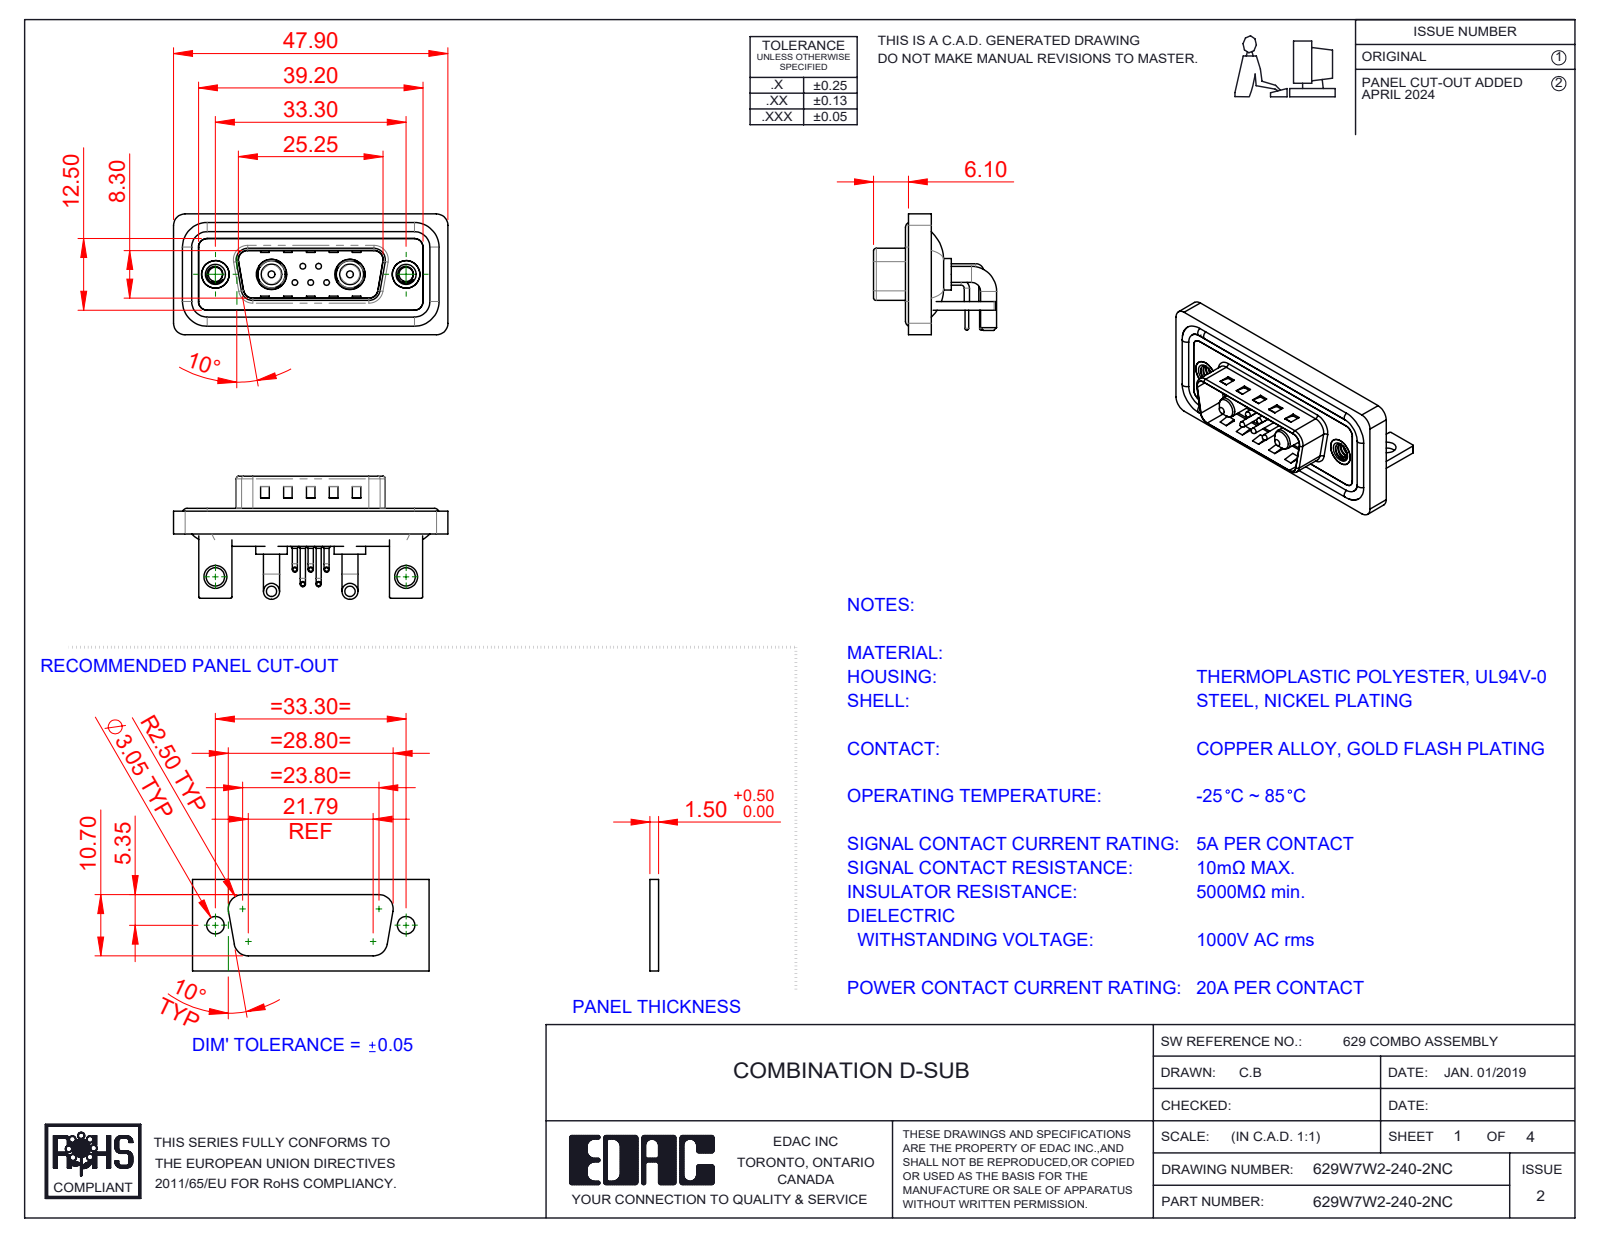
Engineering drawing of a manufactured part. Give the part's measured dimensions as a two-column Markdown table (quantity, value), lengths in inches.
| quantity | value |
| --- | --- |
| part name | 629Combo Contact Row 1; 629Combo Stabilizer Bracket; 629Combo Contact Row 2; 629Combo Waterproof Housing_15 Contacts (+6 more) |
| STEP written by | SolidWorks 2023 (CONFIG_CONTROL_DESIGN) |
| units | inches |
| bodies | 18 solids, 1121 faces (537 planar, 424 cylindrical, 160 other) |
| overall size | 1.886 × 0.846 × 0.831 |
| volume | 0.363 in³ |
| surface area | 15.08 in² |
| round holes (diameter × count) | 0.03 × 5, 0.063 × 5, 0.079 × 5, 0.098 × 2, 0.126 × 2, 0.157 × 2, 0.189 × 2, 0.191 × 2, 0.197 × 2, 0.209 × 2 |
| round bosses / shafts (diameter × count) | 0.035 × 10, 0.059 × 5, 0.039 × 5, 0.026 × 5, 0.11 × 4, 0.063 × 4, 0.217 × 2, 0.205 × 2 |
| partial cylindrical surfaces (radius × count) | 0.079 × 21, 0.059 × 18, 0.01 × 16, 0.02 × 9, 0.063 × 8, 0.04 × 5, 0.024 × 4, 0.026 × 4 |
| main face-to-face distances | 0.016, 0.059, 0.031, 0.114, 0.083, 0.043, 0.063, 0.047, 0.146, 0.177 |
| hole center spacings | 0.124, 0.109, 0.386, 0.925, 1.311, 0.17, 0.17, 0.198 |
